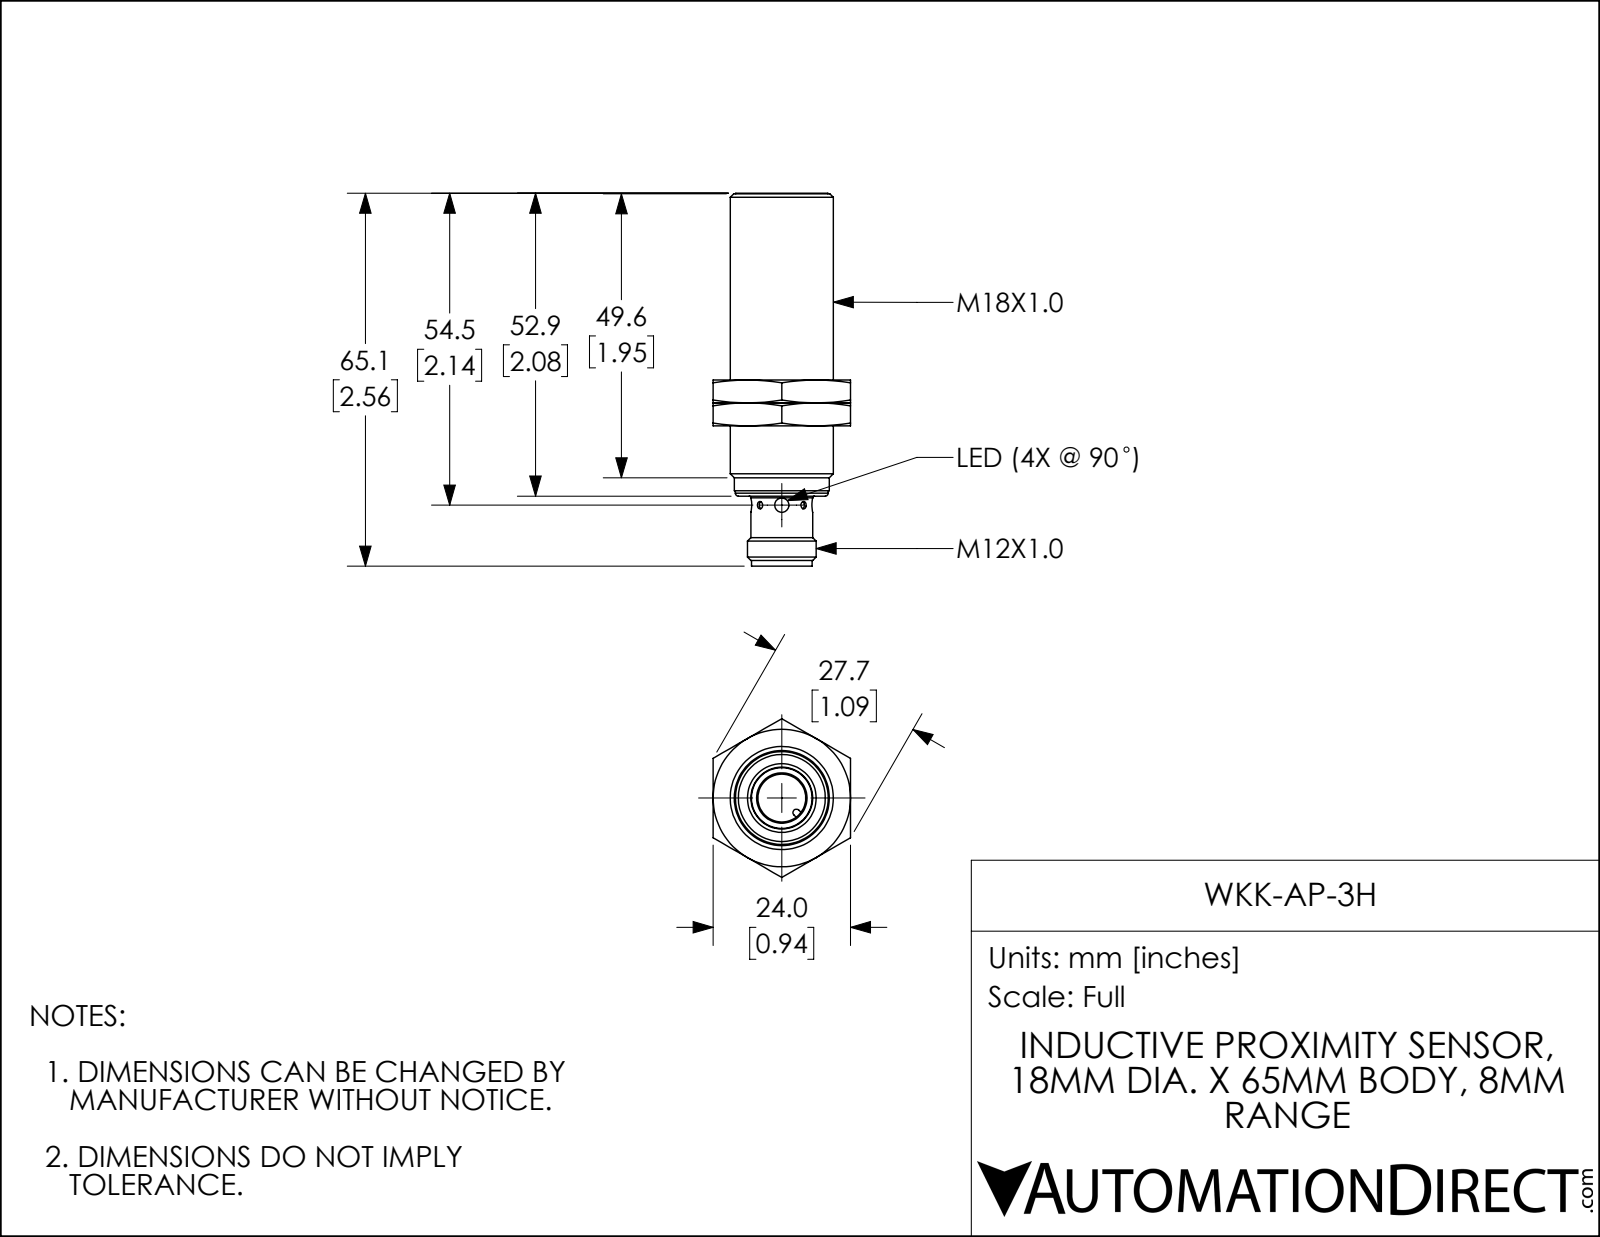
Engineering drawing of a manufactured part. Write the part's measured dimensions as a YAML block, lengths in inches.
part_name: "WKK-AP-3H"
step_written_by: "SolidWorks 2017 (AUTOMOTIVE_DESIGN)"
units: inches
bodies: {solids: 3, faces: 88, planar: 26, cylindrical: 27, other: 35}
overall_size: [2.563, 1.091, 0.945]
volume: 0.984
surface_area: 9.619
round_holes:
  - {diameter: 0.051, count: 2}
  - {diameter: 0.098, count: 2}
  - {diameter: 0.329, count: 1}
  - {diameter: 0.666, count: 1}
round_bosses_or_shafts:
  - {diameter: 0.709, count: 1}
  - {diameter: 0.654, count: 1}
  - {diameter: 0.638, count: 1}
  - {diameter: 0.633, count: 1}
  - {diameter: 0.472, count: 1}
  - {diameter: 0.425, count: 1}
  - {diameter: 0.417, count: 1}
partial_cylinders:
  - {radius: 0.024, count: 1}
  - {radius: 0.195, count: 1}
face_to_face_distances: [0.157, 0.945, 1.441, 0.315, 1.599, 1.284, 0.483, 0.641, 0.798, 2.082]
